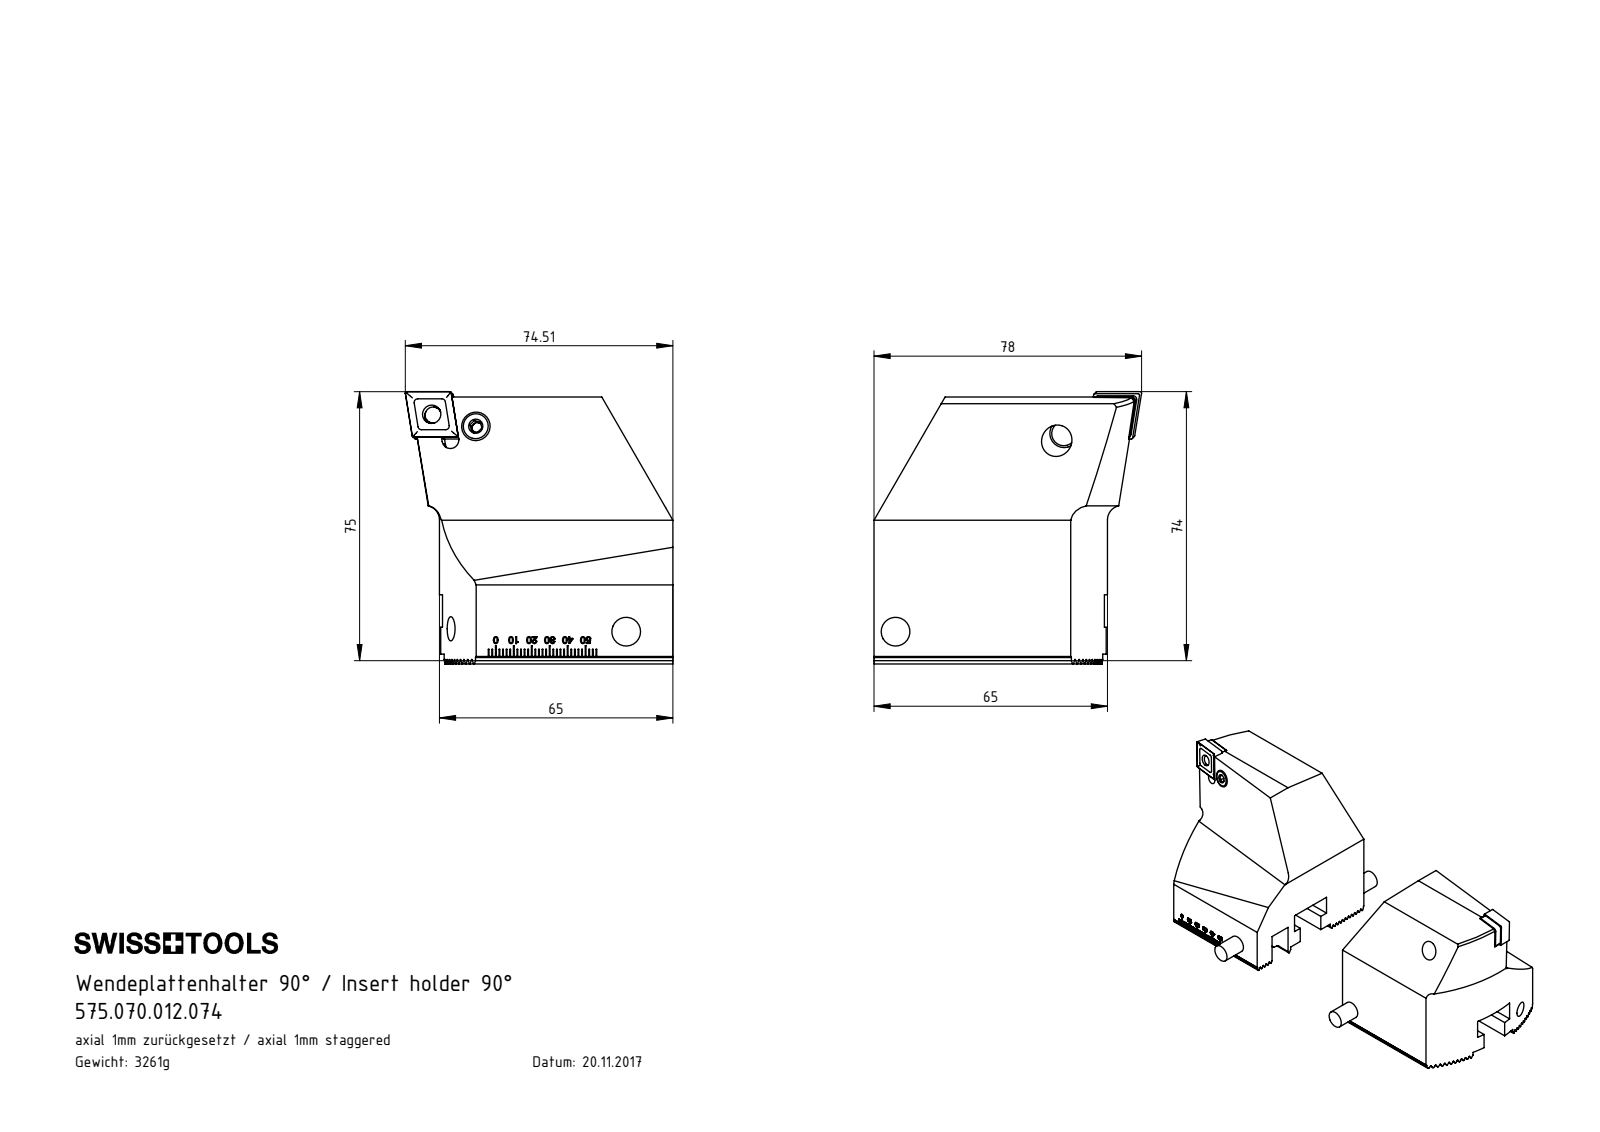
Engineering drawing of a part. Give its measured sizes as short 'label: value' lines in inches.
name: VK1-WCD.B01.075; WCD; ISO 8734 - 8 x 20 m6; WCD-ER1.101.000 (+6 more)
written by: SolidWorks 2017 (CONFIG_CONTROL_DESIGN)
unit: in
bodies: 16 solids, 1263 faces (759 planar, 164 cylindrical, 340 other)
size: 8.071 × 3.701 × 2.984
volume: 25.25 in³; area: 104 in²
holes: 4× ⌀0.315, 2× ⌀0.203, 2× ⌀0.252, 2× ⌀0.268, 2× ⌀0.276, 2× ⌀0.331
bosses: 3× ⌀0.315, 2× ⌀0.311, 2× ⌀0.252, 2× ⌀0.177, 2× ⌀0.14, 1× ⌀0.217
rounds: 22× R0.006, 8× R0.016, 8× R0.039, 6× R0.098, 2× R0.083, 2× R0.087, 2× R0.093, 2× R0.11
face distances: 0.068, 0.341, 0.136, 2.756, 0.273, 0.205, 1.705, 0.965, 1.791, 0.409
hole spacings: 0.276, 0.504, 0.506, 2.953, 1.575, 2.677, 3.228
